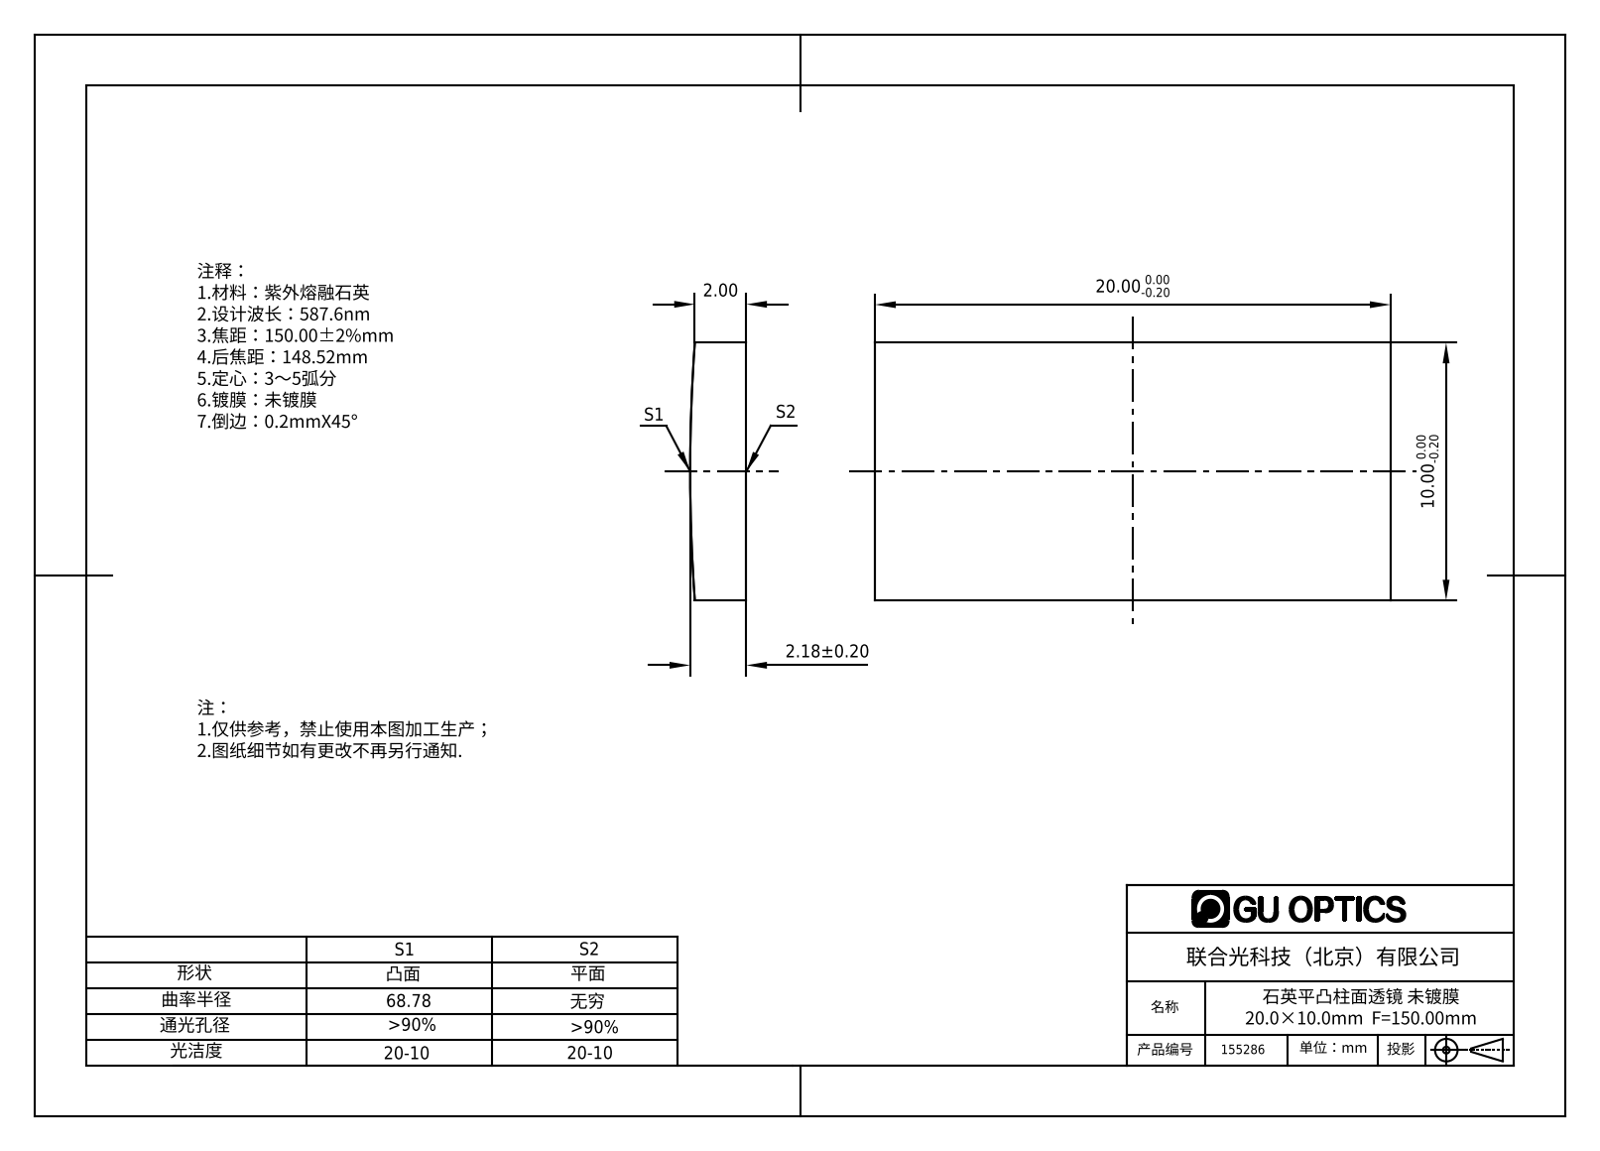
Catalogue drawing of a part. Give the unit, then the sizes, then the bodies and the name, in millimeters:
Units: millimetres
Overall size (bounding box): 20 × 10 × 2.18
Partial cylindrical surfaces — rounded edges, fillets, slot ends (radius × count): R68.78 ×1
Main face-to-face distances: 10, 20
Volume: 424 mm³ · Surface area: 522 mm²
Bodies: 1 solid, 6 faces (5 planar, 1 cylindrical, 0 other)
Part name (STEP PRODUCT): 155286
STEP written by: SolidWorks 2016 (AUTOMOTIVE_DESIGN)
